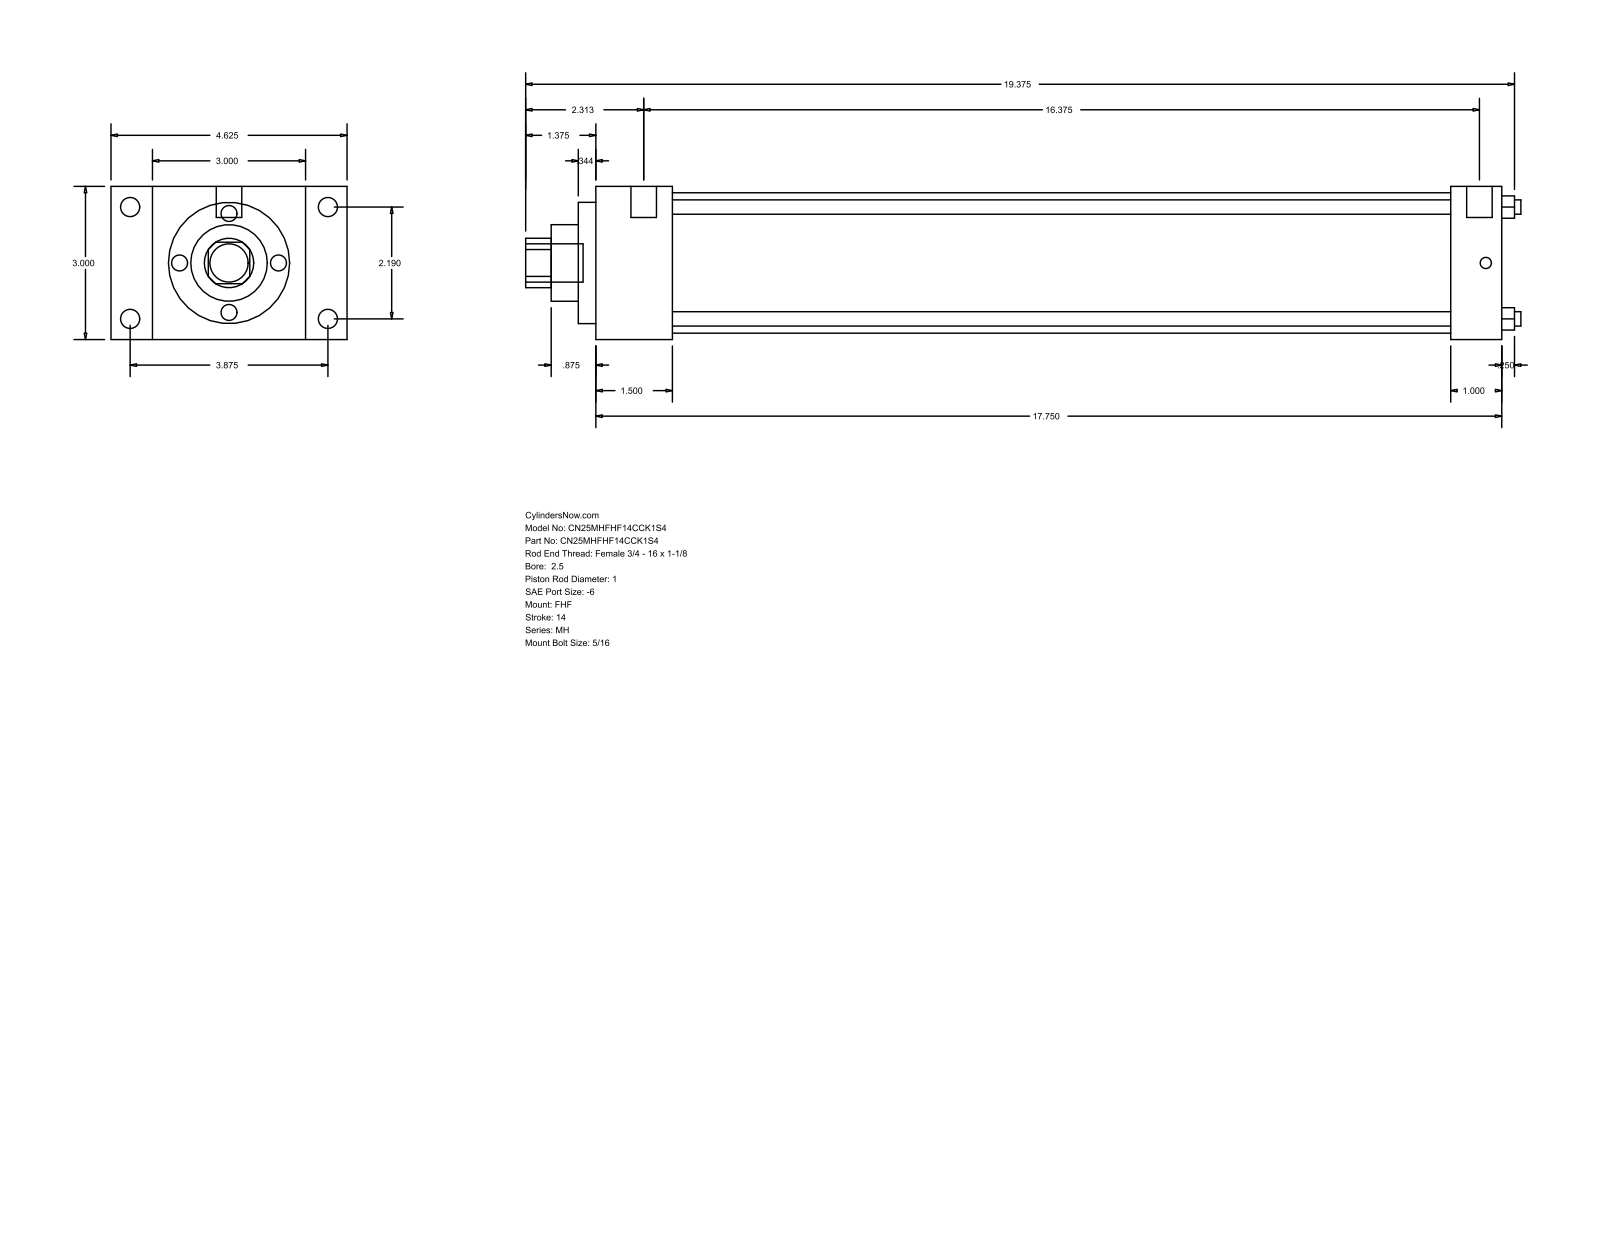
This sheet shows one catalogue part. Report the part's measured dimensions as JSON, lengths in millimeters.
{"part_name": "MH_FHF__0250_1", "step_written_by": "GSSL Pune (CONFIG_CONTROL_DESIGN)", "units": "millimeters", "bodies": {"solids": 0, "faces": 90, "planar": 61, "cylindrical": 29, "other": 0}, "overall_size": [495.3, 117.47, 76.2], "round_holes": [[7.14, 4], [25.4, 1], [38.1, 1], [60.33, 1], [69.85, 1]], "round_bosses_or_shafts": [[9.53, 4], [5.56, 4], [12.7, 2], [19.05, 1]], "partial_cylinders_radius": [[12.29, 1]], "face_to_face_distances": [76.2, 450.85, 38.11, 412.74, 20.64, 96.84, 117.48, 25.39, 425.46, 387.35], "hole_center_spacings": [39.33, 55.62, 78.66]}
